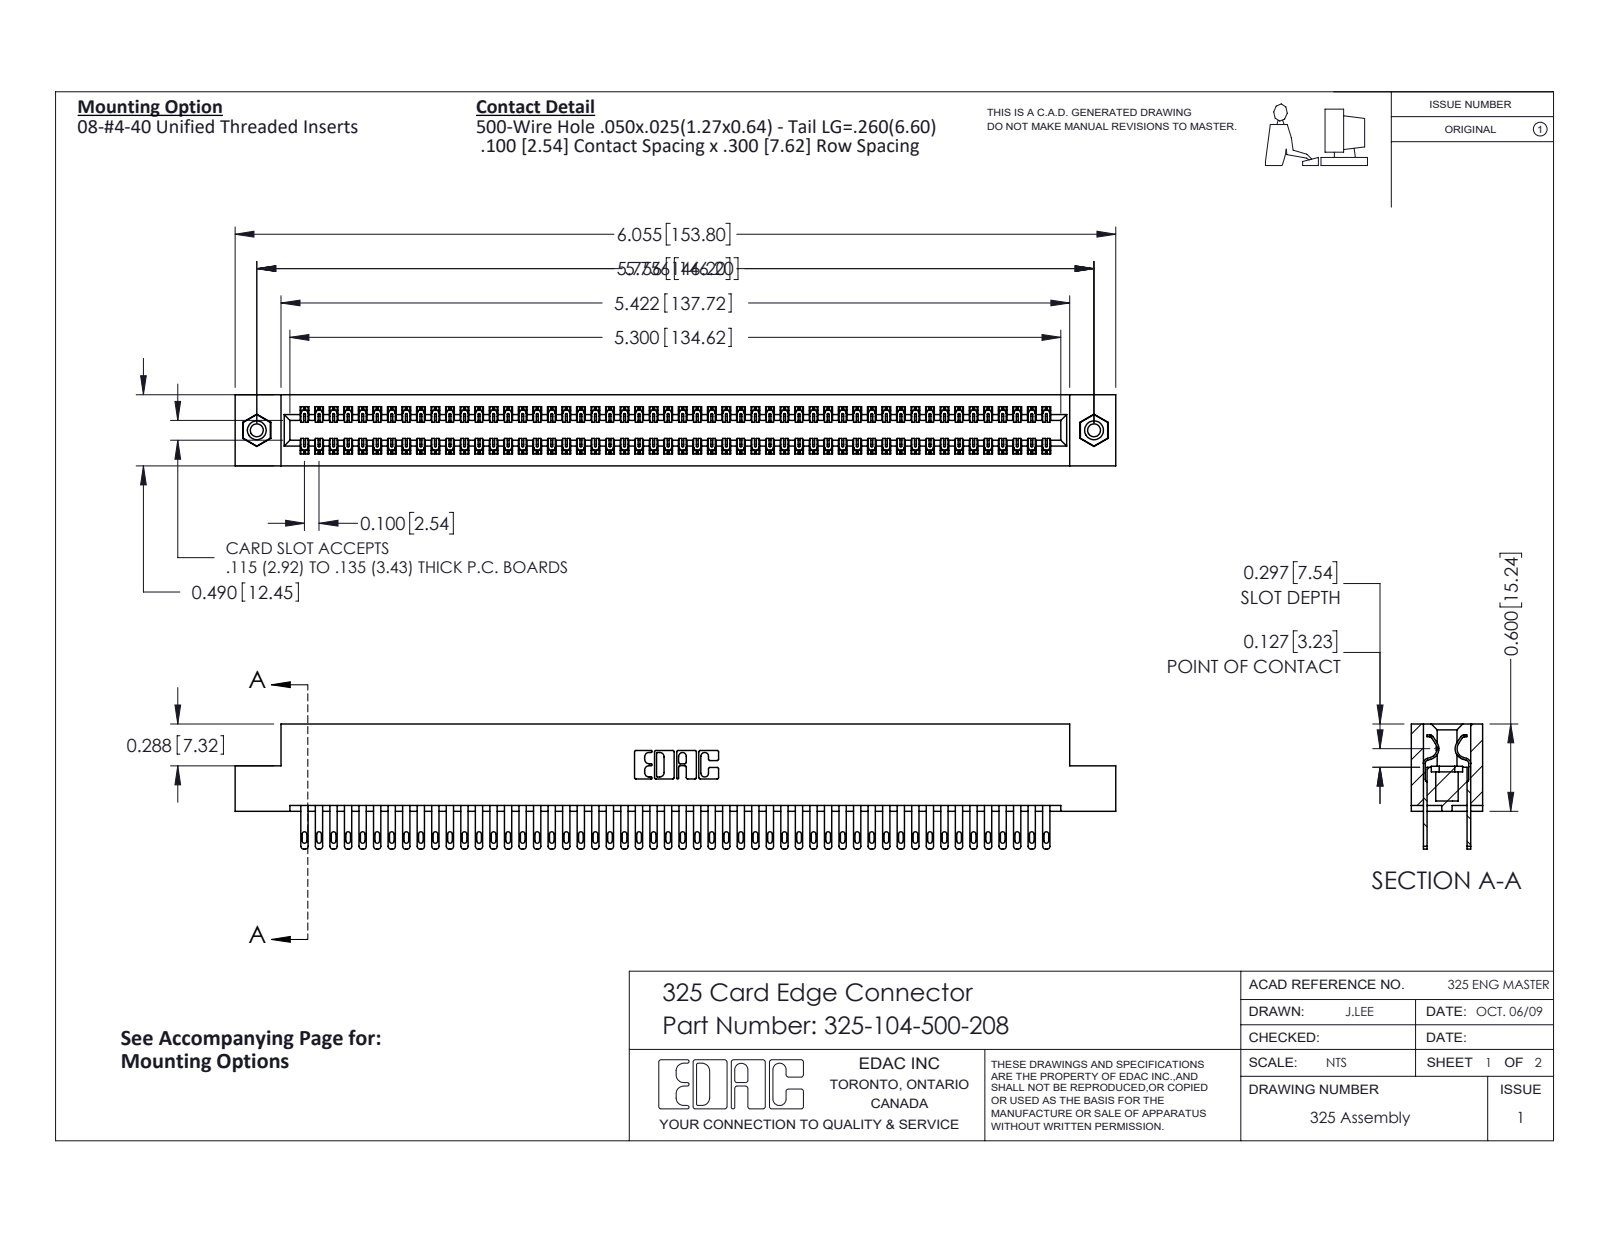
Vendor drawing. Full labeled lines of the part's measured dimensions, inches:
Part name (STEP PRODUCT): 345-250-001_345-250-003-102; 325-292-001_325-293-100; 325-104-500-208; 325 Part_TI
STEP written by: SolidWorks 2016 (CONFIG_CONTROL_DESIGN)
Units: inches
Bodies: 107 solids, 5166 faces (3222 planar, 1928 cylindrical, 16 other)
Overall size (bounding box): 6.055 × 0.86 × 0.49
Volume: 1.236 in³ · Surface area: 40.08 in²
Round holes (diameter × count): ⌀0.089 ×2, ⌀0.125 ×2, ⌀0.16 ×2
Round bosses / shafts (diameter × count): ⌀0.155 ×2
Partial cylindrical surfaces — rounded edges, fillets, slot ends (radius × count): R0.006 ×156, R0.016 ×104, R0.02 ×104, R0.01 ×22, R0.007 ×6, R0.031 ×6, R0.026 ×3, R0.014 ×2
Main face-to-face distances: 0.083, 0.407, 0.3, 0.107, 0.383, 0.025, 0.49, 0.325, 0.275, 0.56
Hole centre spacings: 5.756
